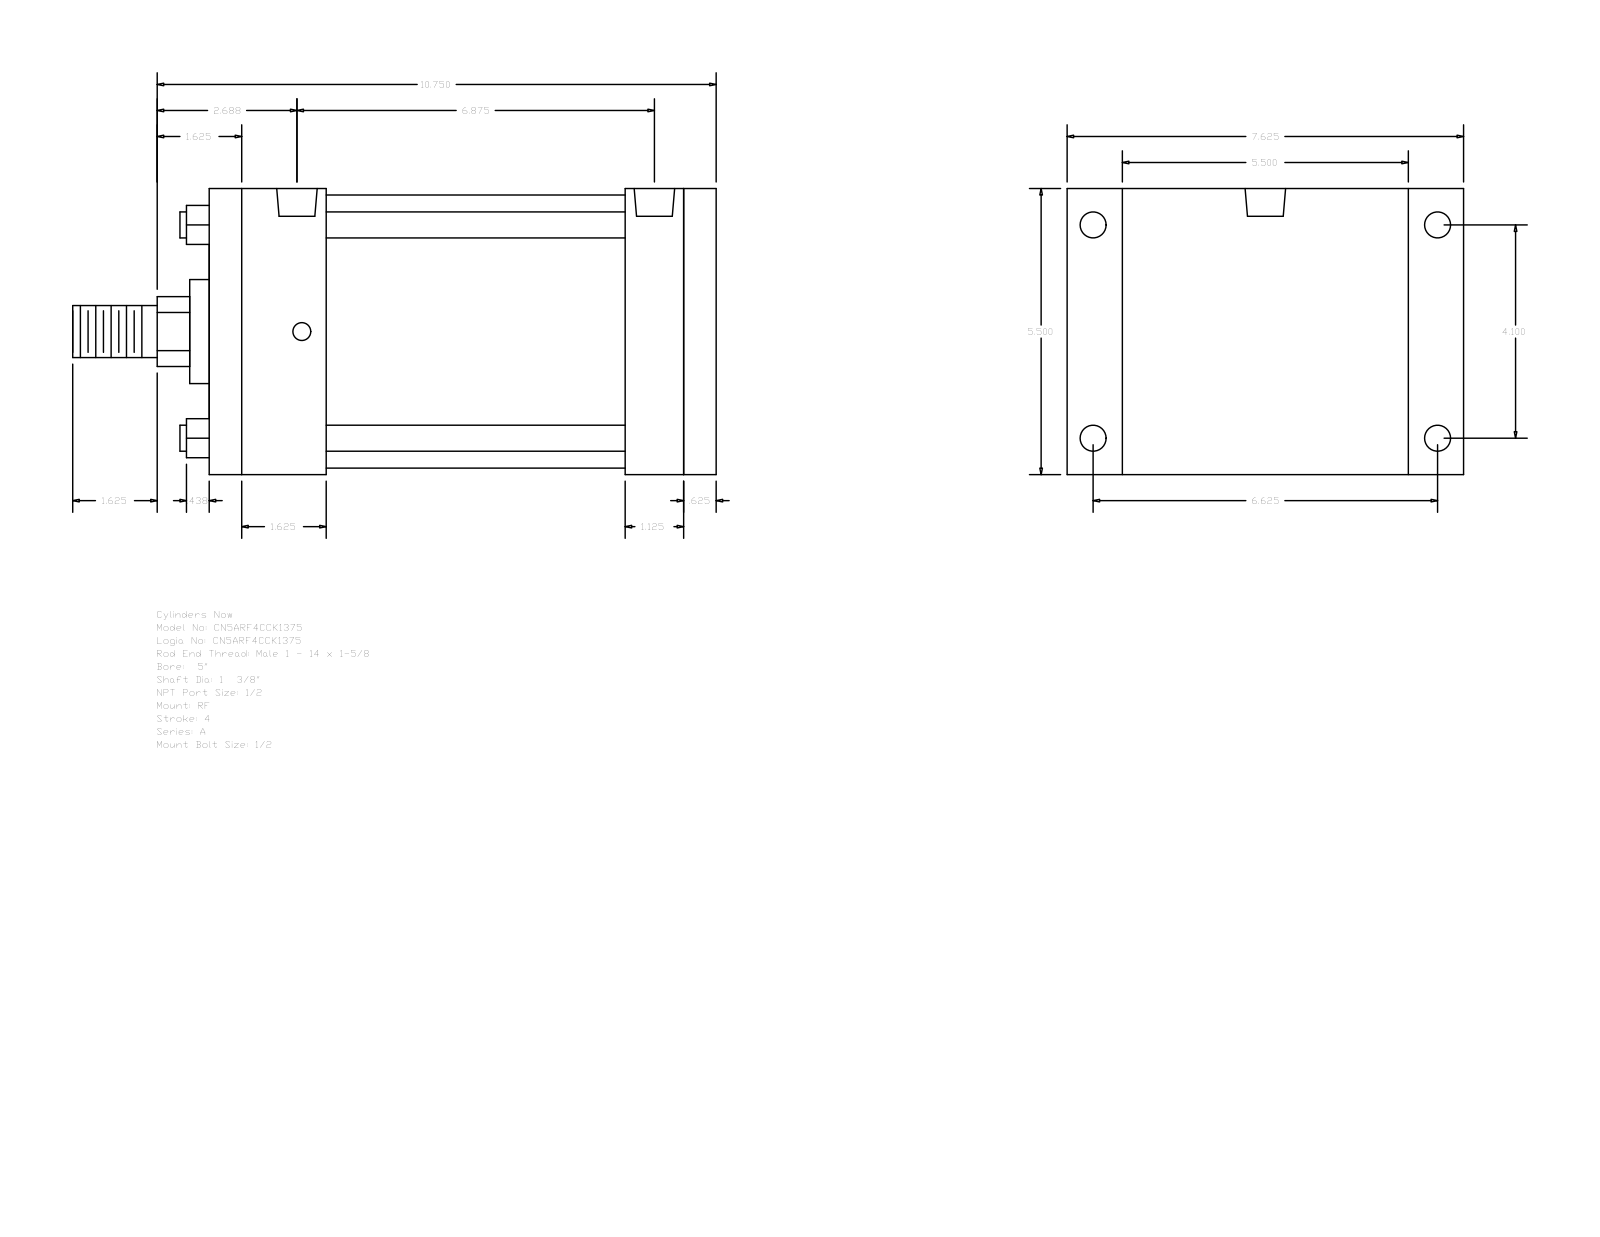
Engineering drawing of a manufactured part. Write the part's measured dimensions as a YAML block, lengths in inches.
part_name: "A_RF__0500_1.375"
step_written_by: "GSSL Pune (CONFIG_CONTROL_DESIGN)"
units: inches
bodies: {solids: 0, faces: 92, planar: 64, cylindrical: 28, other: 0}
overall_size: [12.375, 7.625, 5.5]
round_holes:
  - {diameter: 0.344, count: 4}
  - {diameter: 0.5, count: 4}
  - {diameter: 0.778, count: 2}
round_bosses_or_shafts:
  - {diameter: 0.5, count: 4}
  - {diameter: 5.25, count: 1}
  - {diameter: 2, count: 1}
  - {diameter: 1.375, count: 1}
  - {diameter: 1, count: 1}
partial_cylinders:
  - {radius: 0.672, count: 1}
face_to_face_distances: [5.5, 9.75, 9.125, 0.625, 2.25, 1.125, 6.875, 7.5, 8, 5.75]
hole_center_spacings: [0.094, 4.1, 6.625, 6.687, 6.781, 7.791, 6.875]
